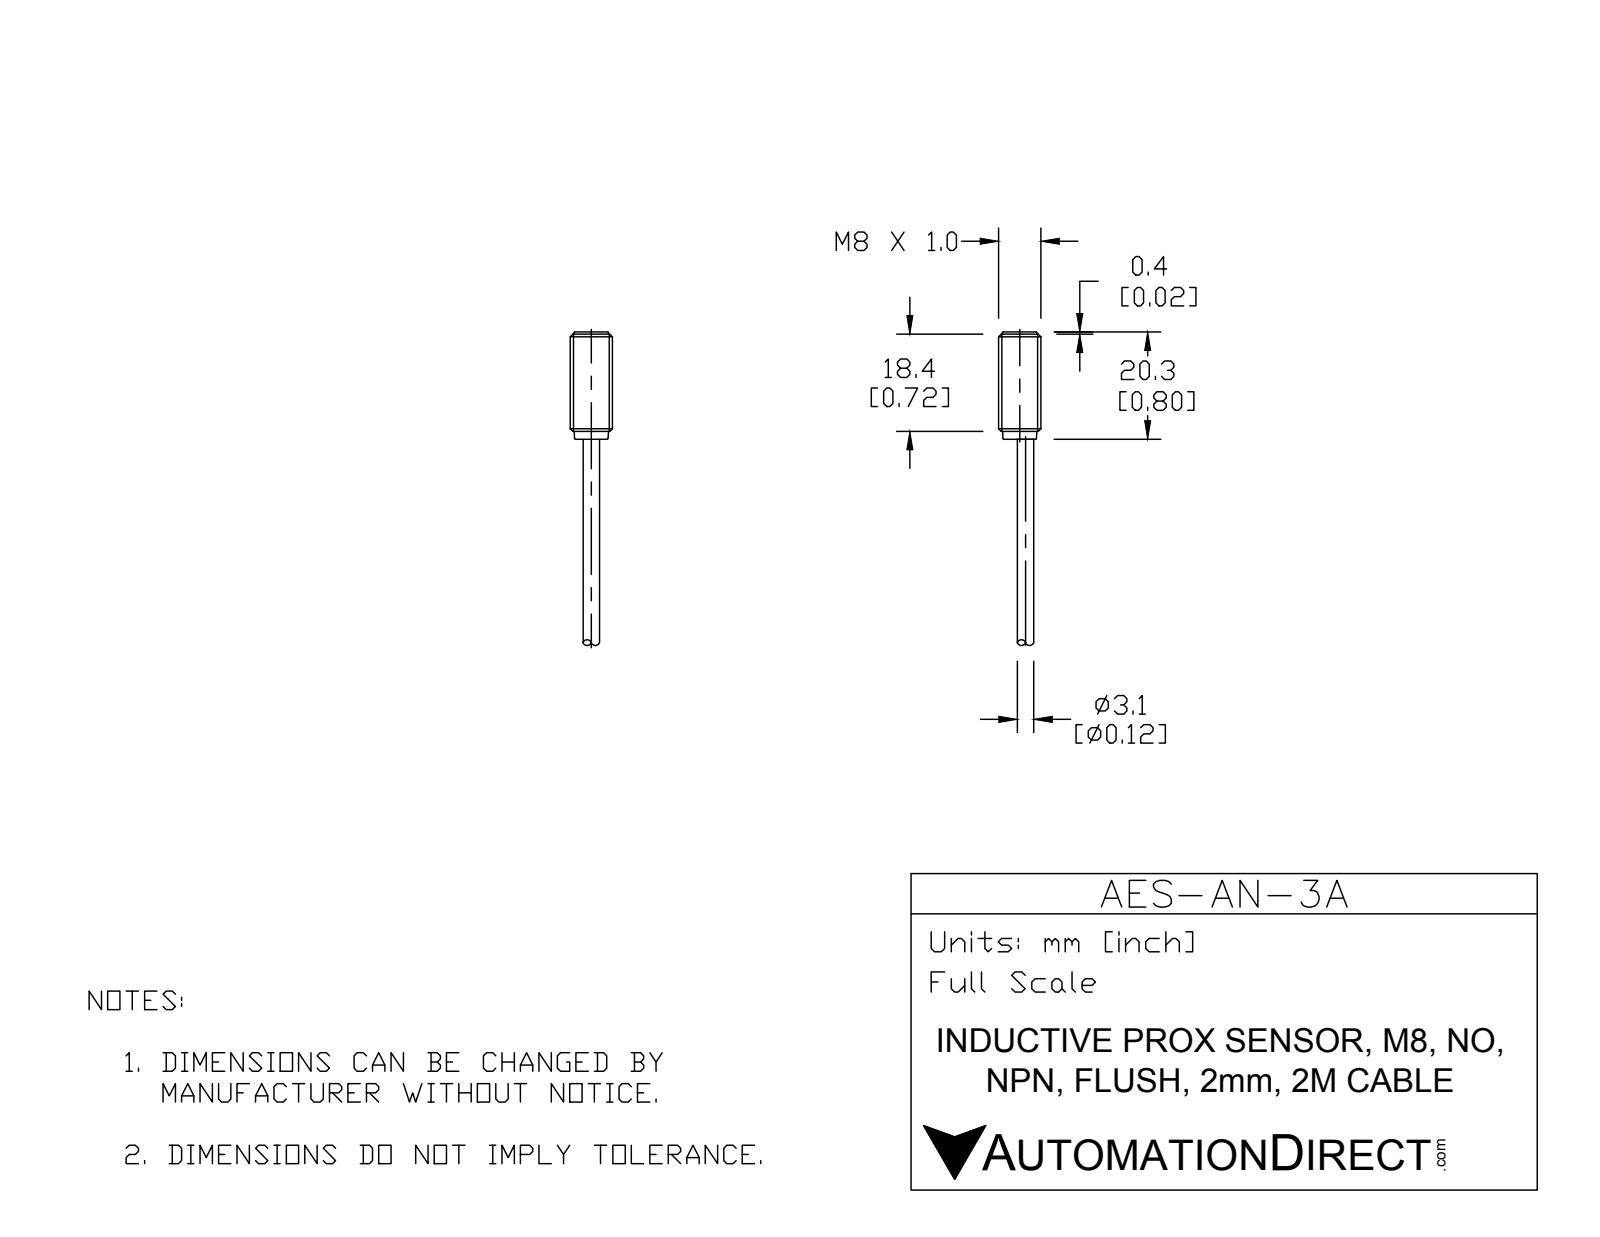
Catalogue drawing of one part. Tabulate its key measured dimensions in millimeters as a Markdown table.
| quantity | value |
| --- | --- |
| part name | AES-AN-3A |
| STEP written by | SolidWorks 2015 (CONFIG_CONTROL_DESIGN) |
| units | millimeters |
| bodies | 1 solid, 21 faces (5 planar, 6 cylindrical, 10 other) |
| overall size | 69.9 × 8 × 8 |
| volume | 1 335 mm³ |
| surface area | 1 054 mm² |
| round bosses / shafts (diameter × count) | 8 × 1, 6.5 × 1, 3.1 × 1 |
| main face-to-face distances | 19.9, 50, 69.9, 69.5, 19.5, 0.4, 51.5, 1.5, 18, 18.4 |
